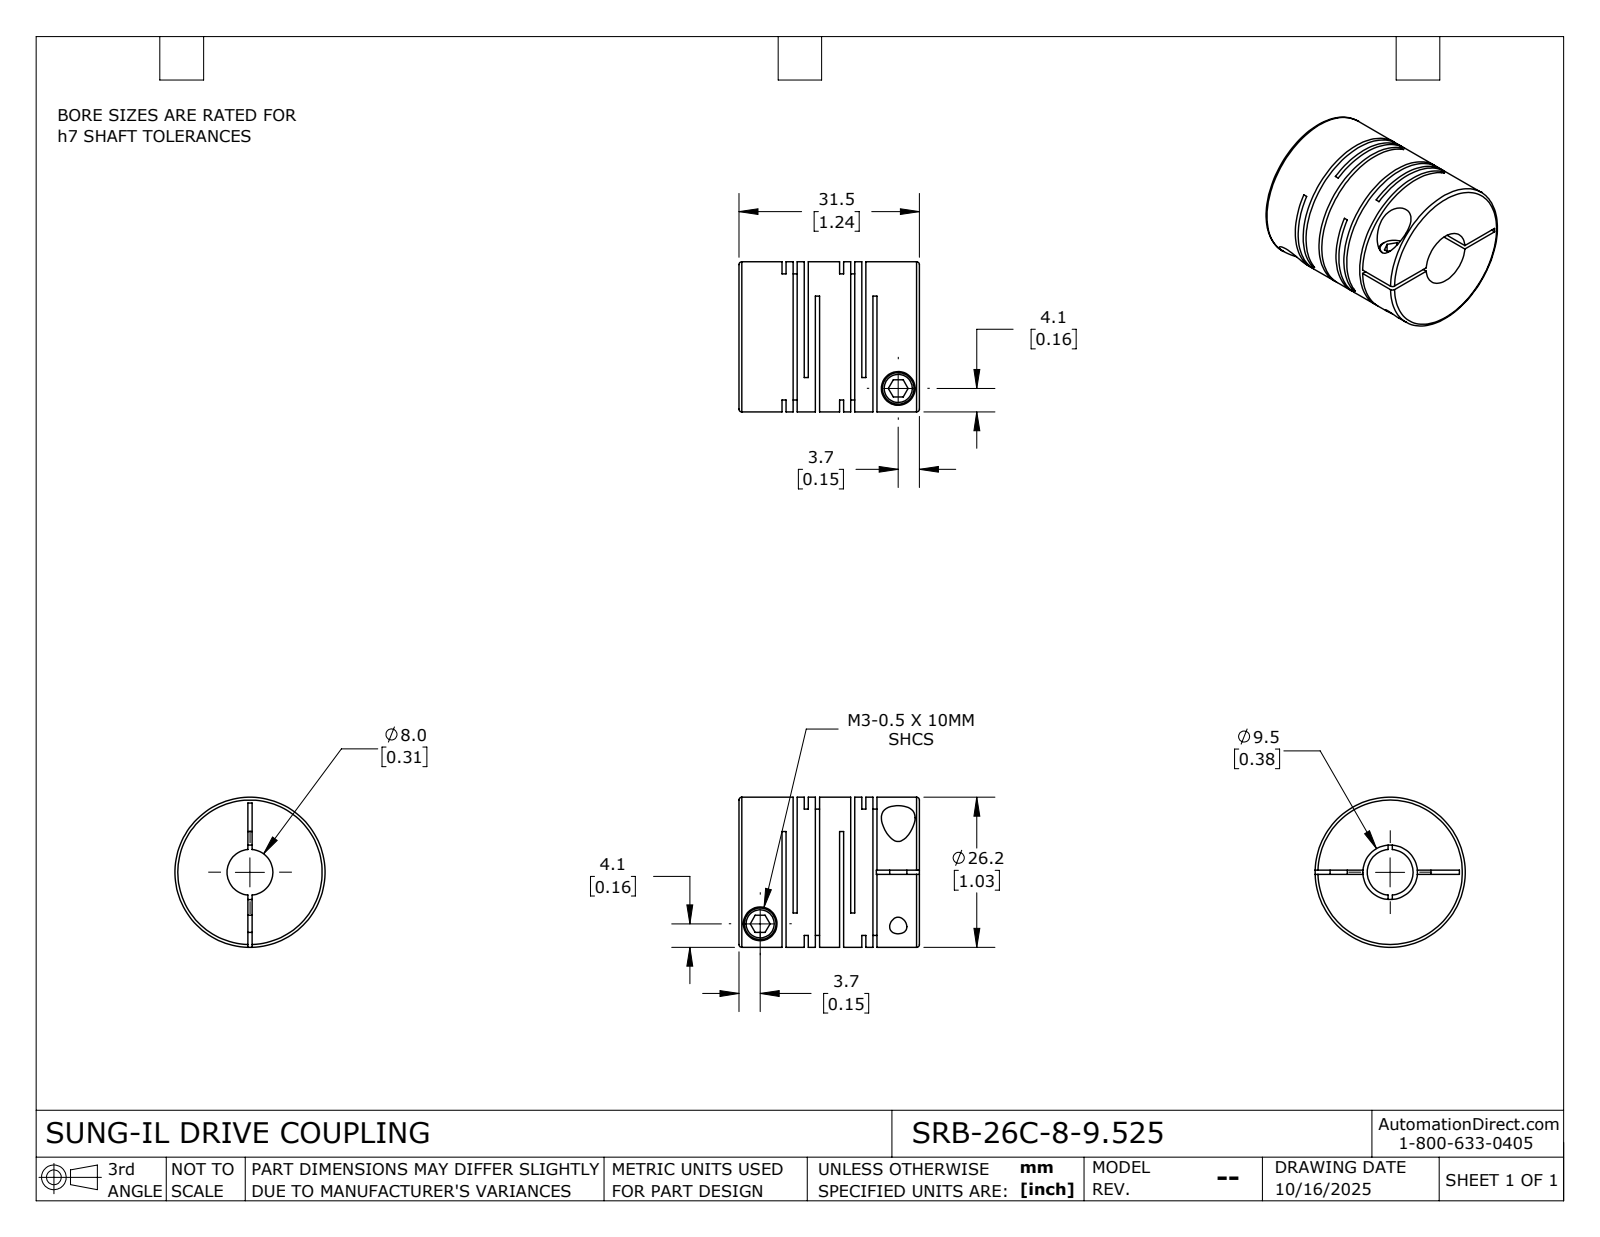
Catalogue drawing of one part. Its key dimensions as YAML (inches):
part_name: "SRB-26C-8-9.525"
step_written_by: "SolidWorks 2024 (CONFIG_CONTROL_DESIGN)"
units: inches
bodies: {solids: 1, faces: 115, planar: 60, cylindrical: 42, other: 13}
overall_size: [1.24, 1.031, 1.031]
volume: 0.749
surface_area: 16.83
round_holes:
  - {diameter: 0.118, count: 2}
  - {diameter: 0.232, count: 2}
  - {diameter: 0.315, count: 1}
  - {diameter: 0.375, count: 1}
round_bosses_or_shafts:
  - {diameter: 0.217, count: 2}
  - {diameter: 1.031, count: 1}
face_to_face_distances: [0.077, 0.396, 0.028, 0.154, 0.319, 0.472, 0.049, 0.105, 0.368, 0.549]
